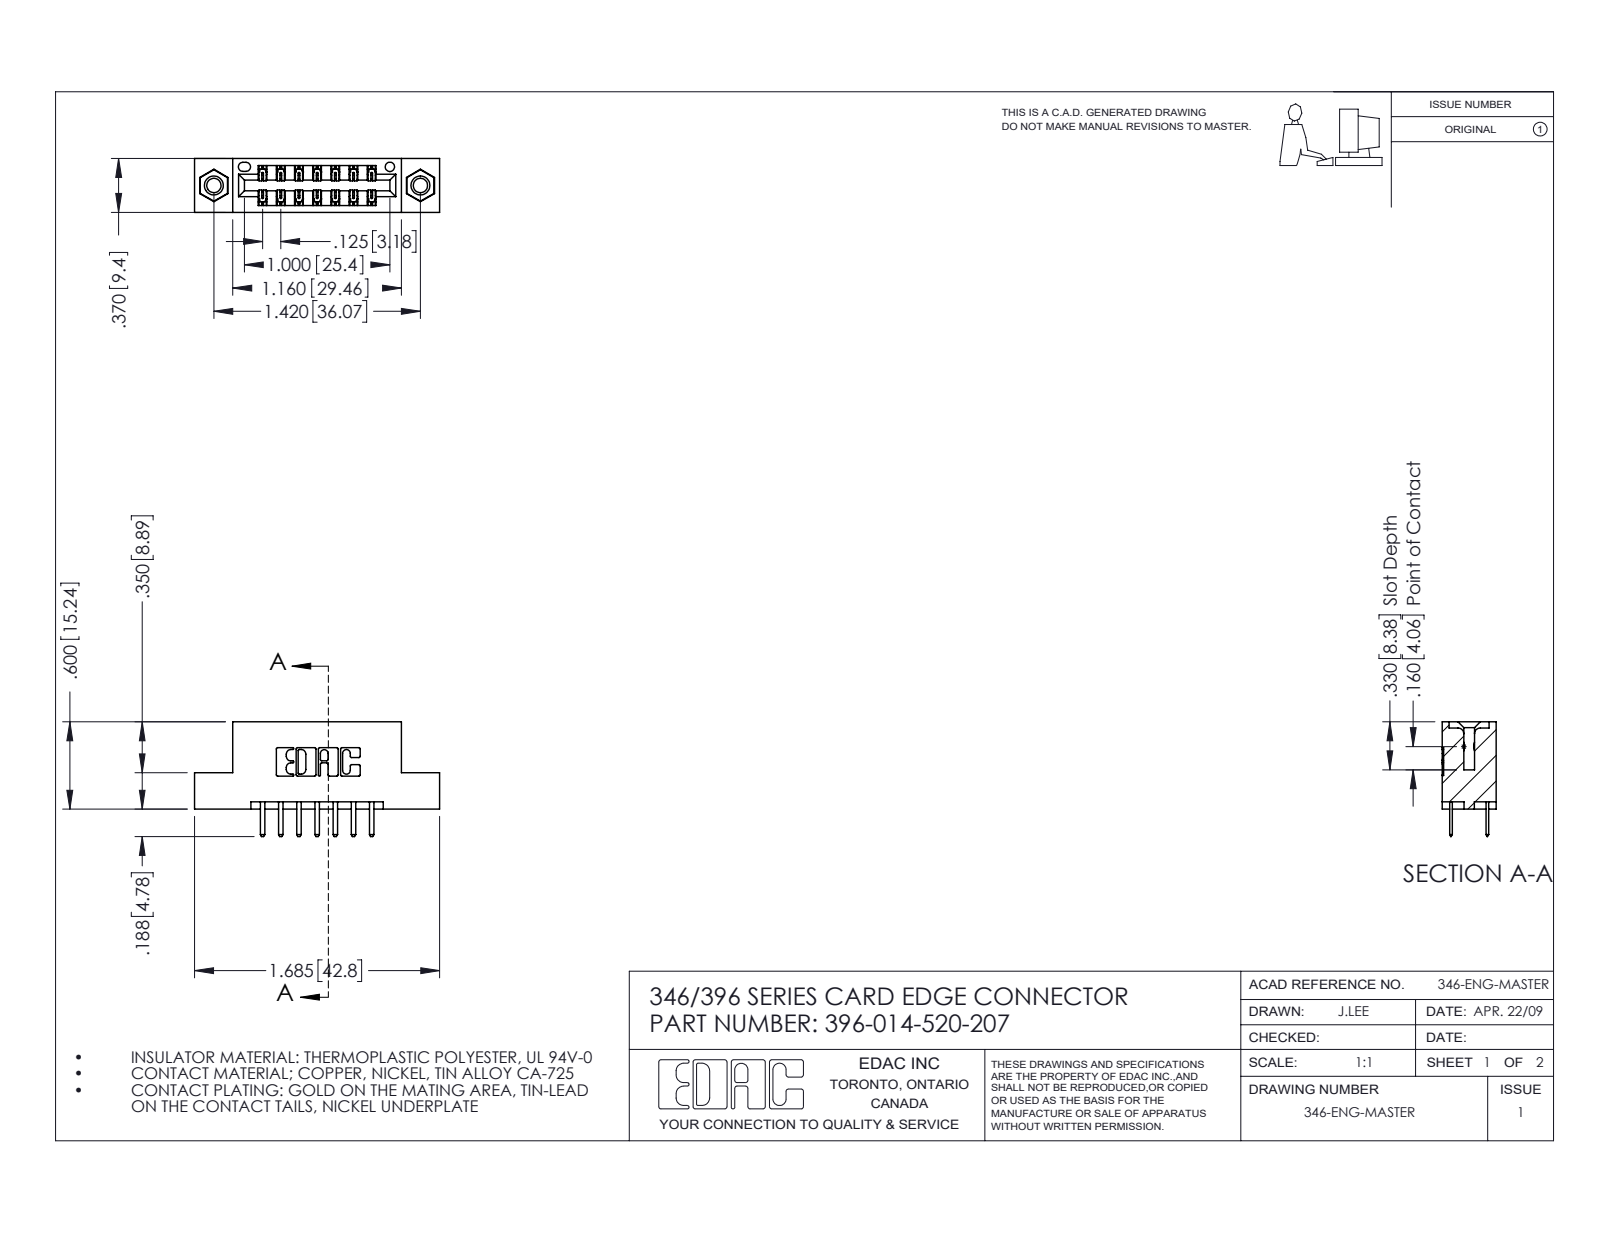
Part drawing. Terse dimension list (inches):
name: 345-250-001_345-250-005-103; 396-014-520-207; 345-292-001_345-293-120; 346 Part_Flush Mounting Lugs - 0.156 Dia-TI
written by: SolidWorks 2016 (CONFIG_CONTROL_DESIGN)
unit: in
bodies: 17 solids, 966 faces (626 planar, 324 cylindrical, 16 other)
size: 1.685 × 0.788 × 0.37
volume: 0.237 in³; area: 7.448 in²
holes: 2× ⌀0.098, 2× ⌀0.125, 2× ⌀0.156, 1× ⌀0.064
bosses: 2× ⌀0.155
rounds: 22× R0.01, 21× R0.006, 18× R0.01, 6× R0.007, 6× R0.031, 3× R0.026, 2× R0.014, 2× R0.022
face distances: 0.25, 0.37, 0.048, 0.322, 0.148, 0.222, 0.1, 0.174, 0.125, 0.185
hole spacings: 0.246, 1.217, 1.42
